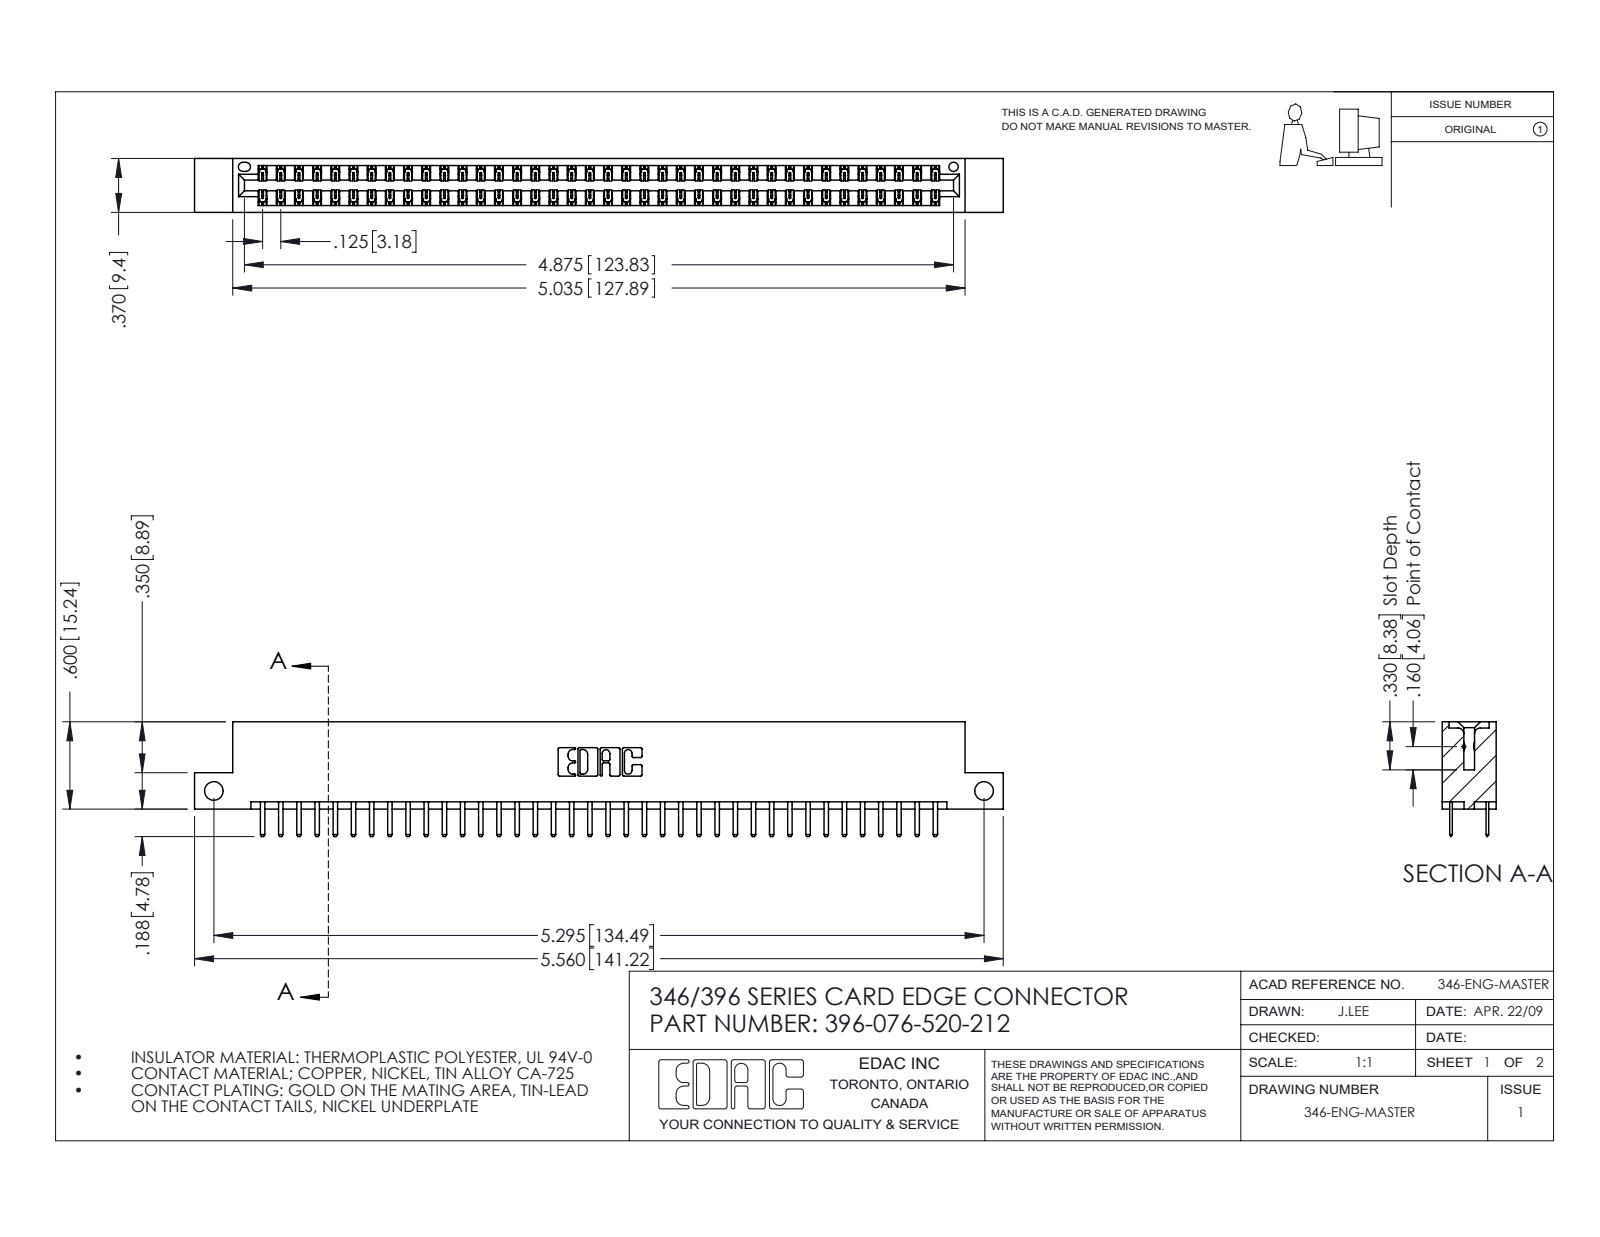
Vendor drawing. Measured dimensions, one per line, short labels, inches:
name: 396-076-520-212; 346 Part_Flush Mounting Lugs - Side Mount; 345-292-001_345-293-120
written by: SolidWorks 2016 (CONFIG_CONTROL_DESIGN)
unit: in
bodies: 77 solids, 4378 faces (2888 planar, 1490 cylindrical, 0 other)
size: 5.56 × 0.788 × 0.37
volume: 0.831 in³; area: 28.59 in²
holes: 2× ⌀0.128, 1× ⌀0.064
rounds: 114× R0.006, 80× R0.01, 22× R0.01, 6× R0.007, 6× R0.031, 3× R0.026, 2× R0.014, 2× R0.022
face distances: 0.048, 0.322, 0.25, 0.37, 0.275, 0.072, 0.298, 0.025, 0.148, 0.222
hole spacings: 5.295
